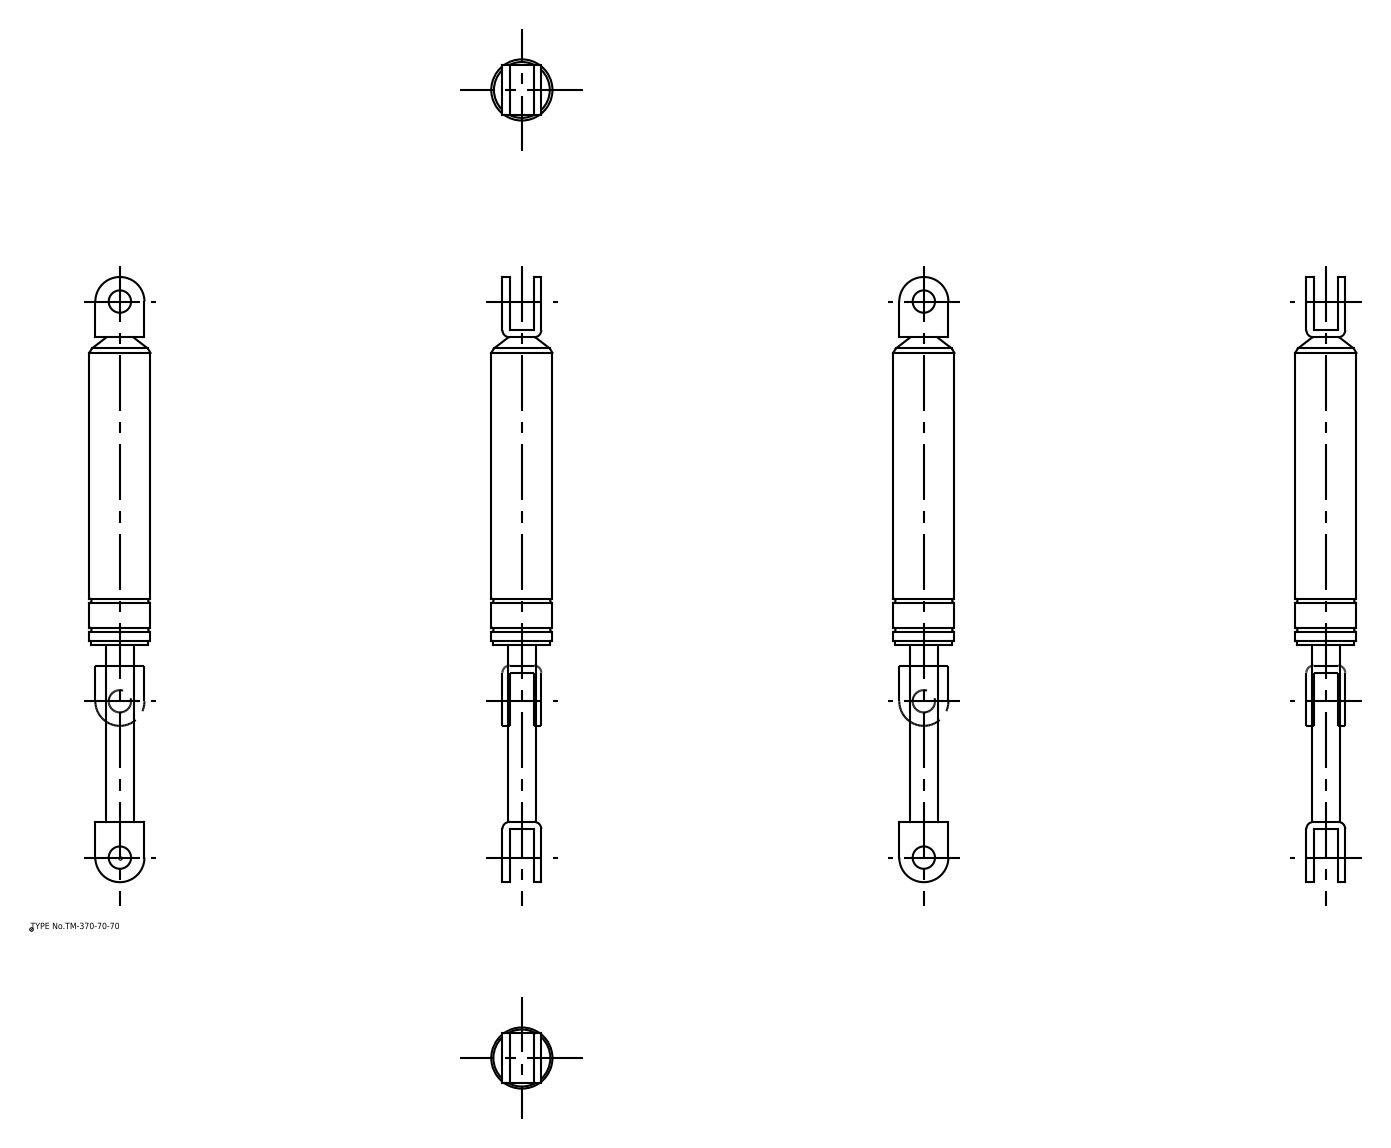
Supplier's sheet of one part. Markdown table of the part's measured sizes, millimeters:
| quantity | value |
| --- | --- |
| part name | TM_370_70_70; TM_370_70_70_div |
| STEP written by | spGate 16.7.1 (AUTOMOTIVE_DESIGN) |
| units | millimeters |
| bodies | 2 solids, 64 faces (22 planar, 32 cylindrical, 10 other) |
| overall size | 271 × 28.2 × 28.2 |
| volume | 96 750 mm³ |
| surface area | 21 763 mm² |
| round holes (diameter × count) | 10 × 2 |
| round bosses / shafts (diameter × count) | 28.2 × 1, 27.4 × 1, 25.5 × 1, 12.5 × 1 |
| partial cylindrical surfaces (radius × count) | 3.2 × 4, 11 × 2 |
| main face-to-face distances | 3.2, 14.2, 17.4, 11, 22, 220.2, 82.2, 223.4, 141.2, 138 |
| hole center spacings | 249 |
